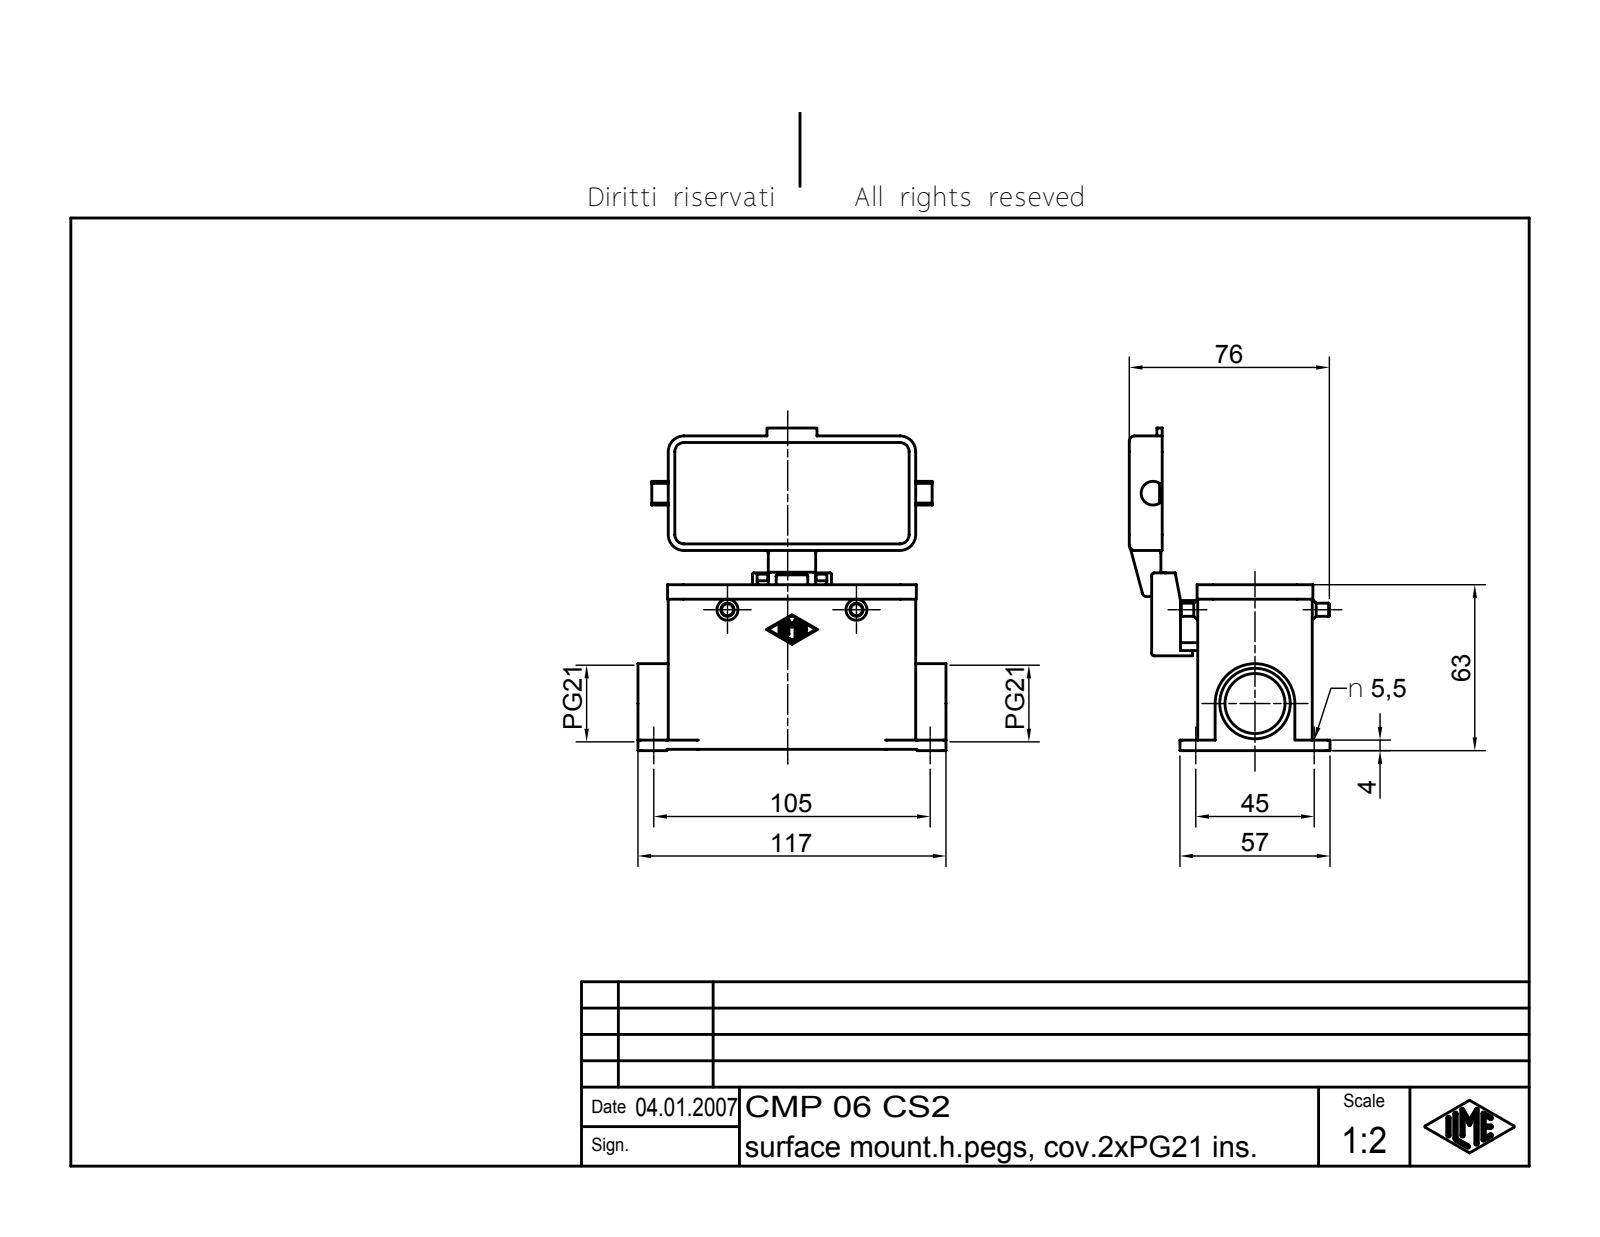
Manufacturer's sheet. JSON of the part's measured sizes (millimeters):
{"part_name": "CMP 06 CS2", "step_written_by": "Autodesk Inventor 7 (AUTOMOTIVE_DESIGN)", "units": "millimeters", "bodies": {"solids": 2, "faces": 474, "planar": 177, "cylindrical": 177, "other": 120}, "overall_size": [122.5, 117, 76.25], "volume_mm3": 115475, "surface_area_mm2": 65768, "round_holes": [[5.5, 4], [4, 1], [5, 1], [22.78, 1], [26.78, 1]], "round_bosses_or_shafts": [[5, 2], [3, 2], [7, 1], [4, 1]], "partial_cylinders_radius": [[1, 26], [0.38, 14], [6, 12], [0.5, 9], [0.7, 8], [2, 8], [3, 4], [3.5, 4]], "face_to_face_distances": [3, 40.5, 3.5, 43.5, 29, 63, 37.5, 22.5, 69.5, 66.5], "hole_center_spacings": [45, 105, 114.24]}
